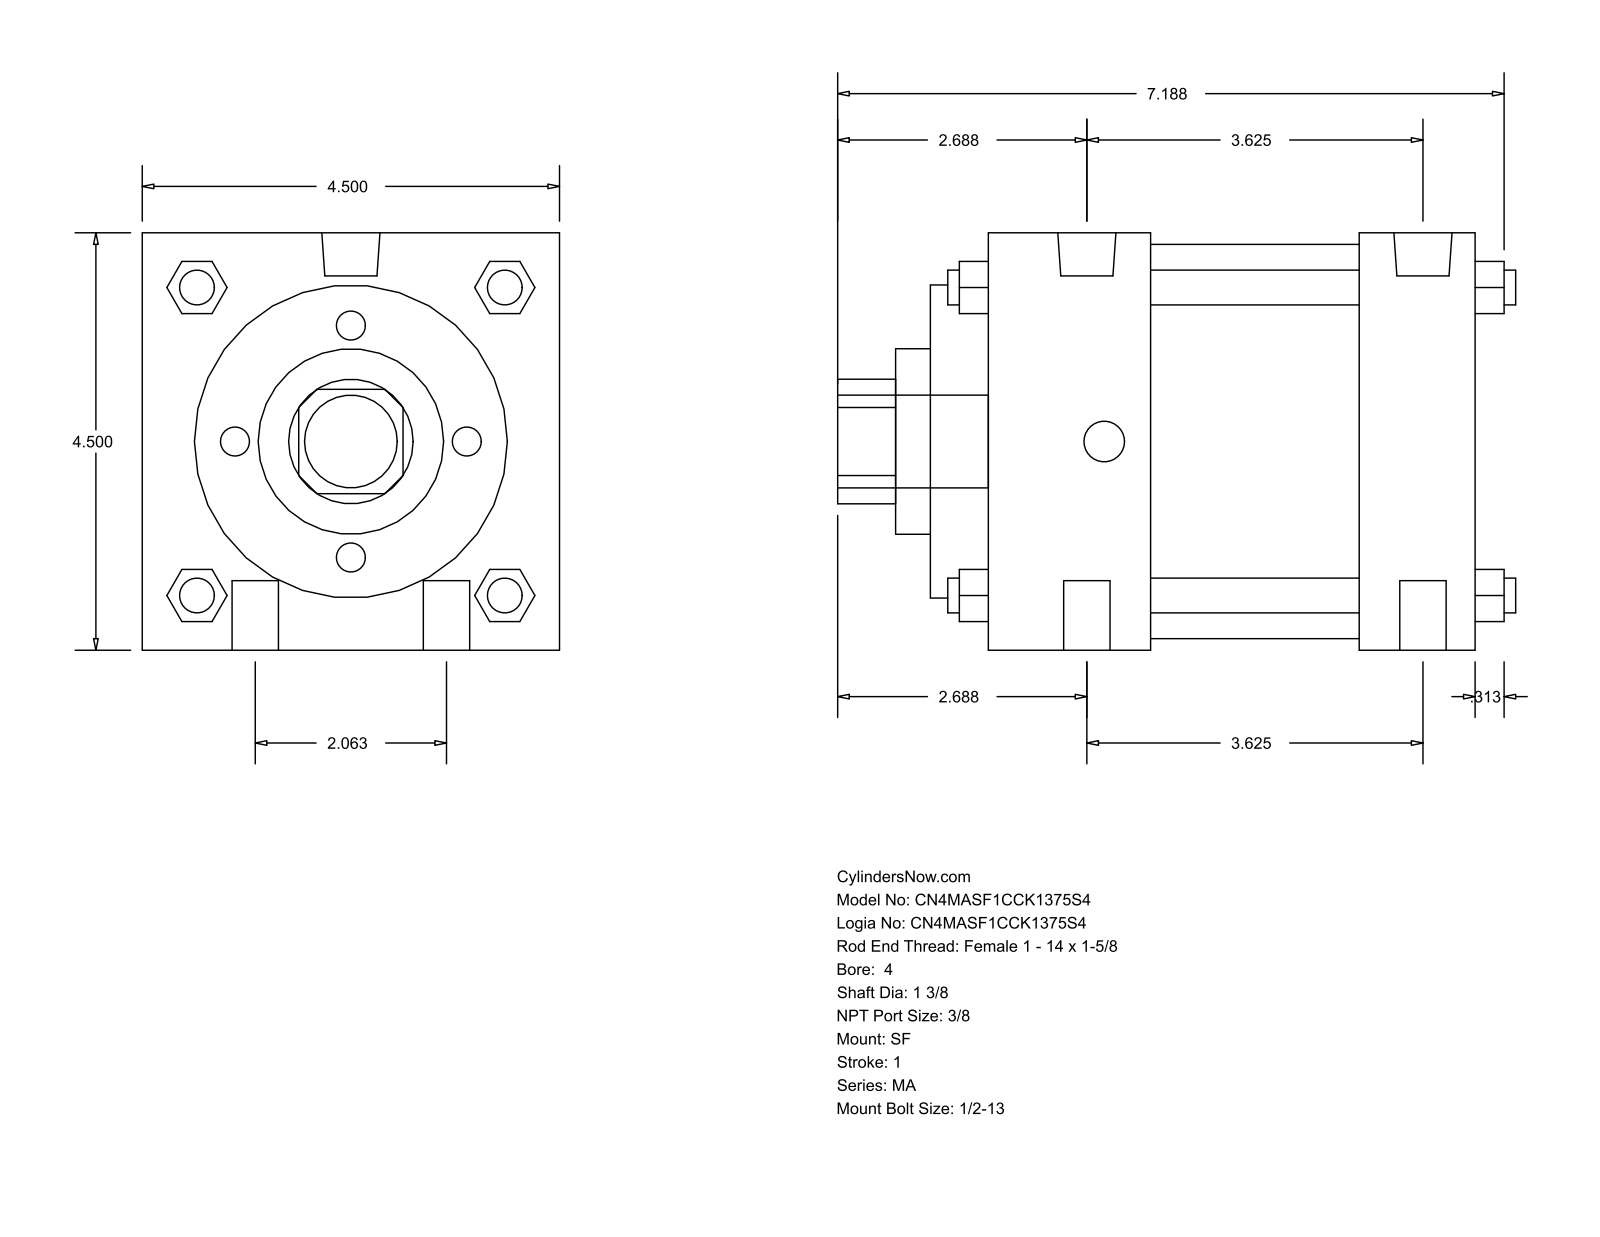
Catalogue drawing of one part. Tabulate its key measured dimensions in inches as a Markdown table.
| quantity | value |
| --- | --- |
| part name | MA_SF__0400_1.375 |
| STEP written by | GSSL Pune (CONFIG_CONTROL_DESIGN) |
| units | inches |
| bodies | 0 solids, 126 faces (95 planar, 31 cylindrical, 0 other) |
| overall size | 7.313 × 4.5 × 4.5 |
| round holes (diameter × count) | 1.375 × 1, 2 × 1, 3.375 × 1, 4.25 × 1 |
| round bosses / shafts (diameter × count) | 0.5 × 4, 0.375 × 4, 0.627 × 2, 0.437 × 2, 1 × 1 |
| partial cylindrical surfaces (radius × count) | 0.672 × 1 |
| main face-to-face distances | 4.5, 5.25, 5.875, 0.625, 4.625, 4, 1.25, 2.375, 1.75, 2.25 |
